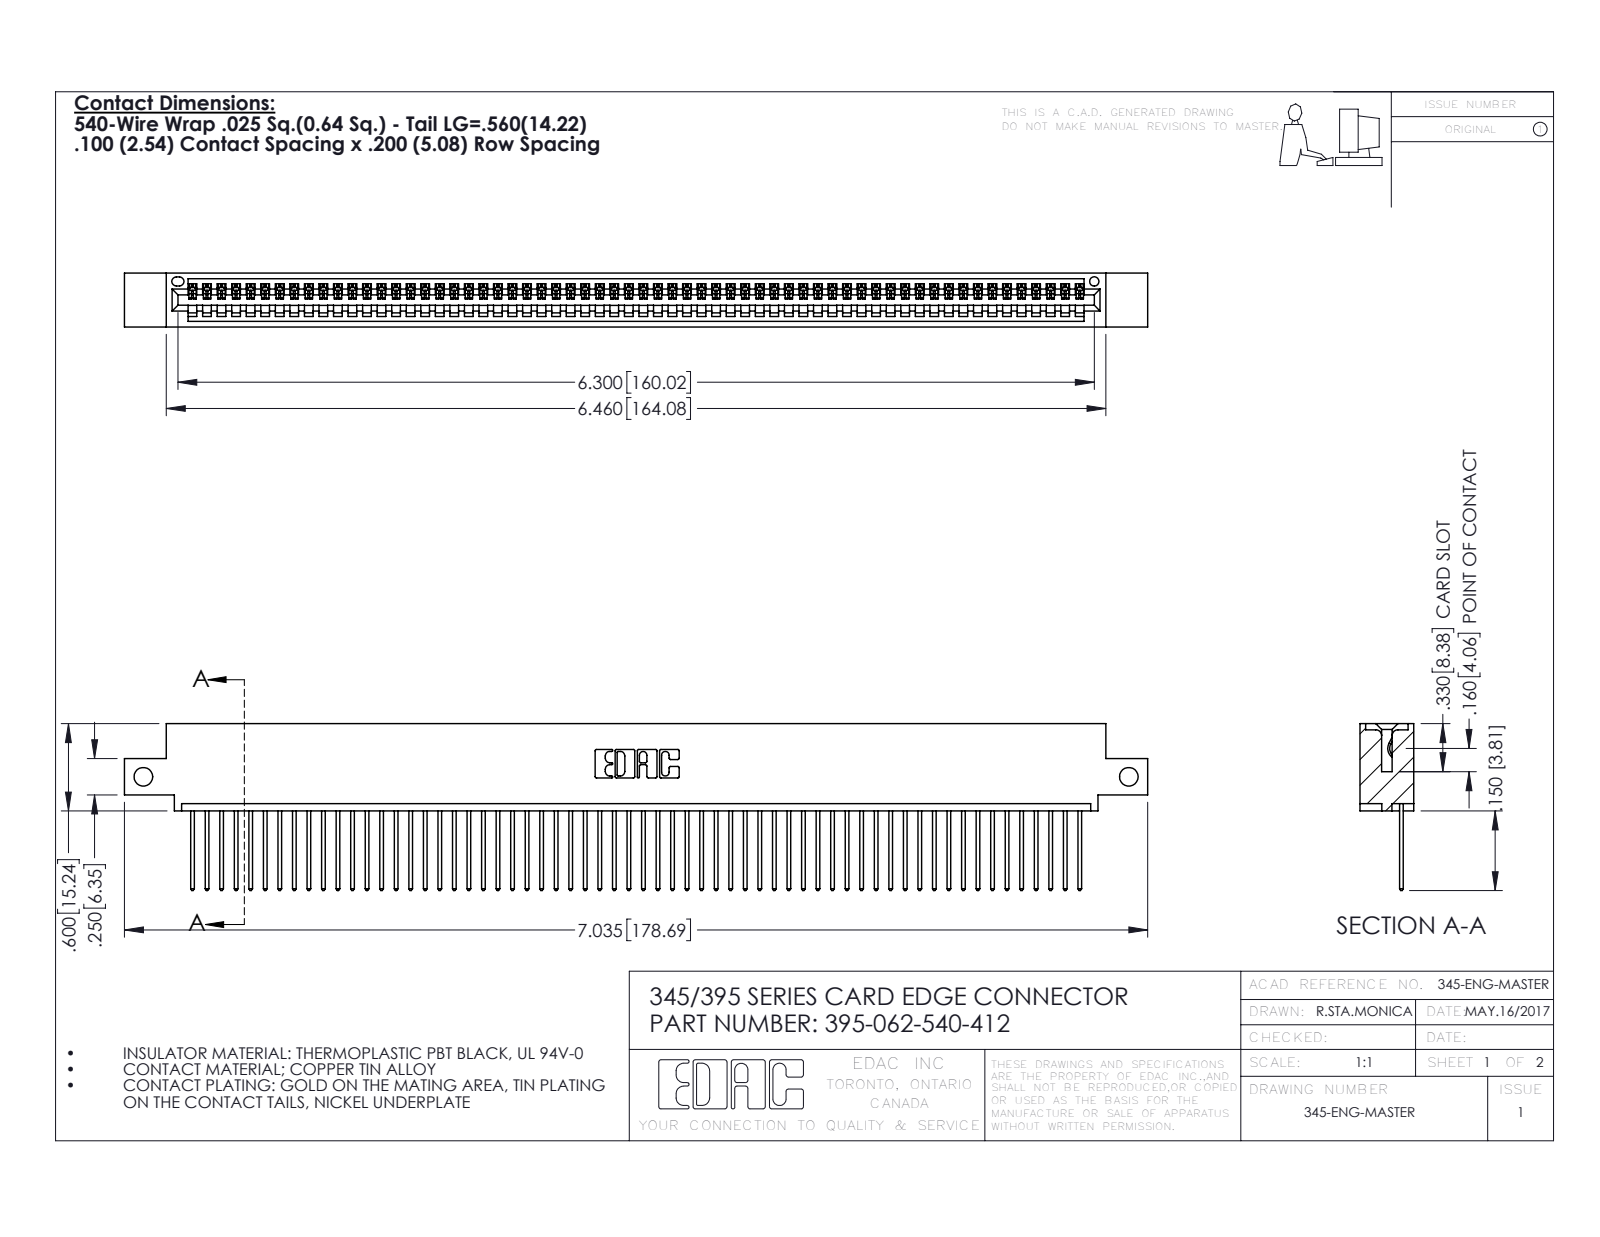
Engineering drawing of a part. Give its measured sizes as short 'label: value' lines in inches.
name: 395-062-540-412; 345-292-001_345-293-140; 345 Part_0.110 Offset - Side Mount
written by: SolidWorks 2016 (CONFIG_CONTROL_DESIGN)
unit: in
bodies: 63 solids, 3726 faces (2564 planar, 1162 cylindrical, 0 other)
size: 7.035 × 1.147 × 0.37
volume: 1.041 in³; area: 36.4 in²
holes: 2× ⌀0.128, 1× ⌀0.064
rounds: 124× R0.006, 124× R0.01, 22× R0.01, 6× R0.007, 6× R0.031, 3× R0.026, 2× R0.031, 2× R0.04
face distances: 0.072, 0.298, 0.37, 0.098, 0.272, 0.025, 0.2, 0.225, 0.149, 0.072
hole spacings: 6.775
